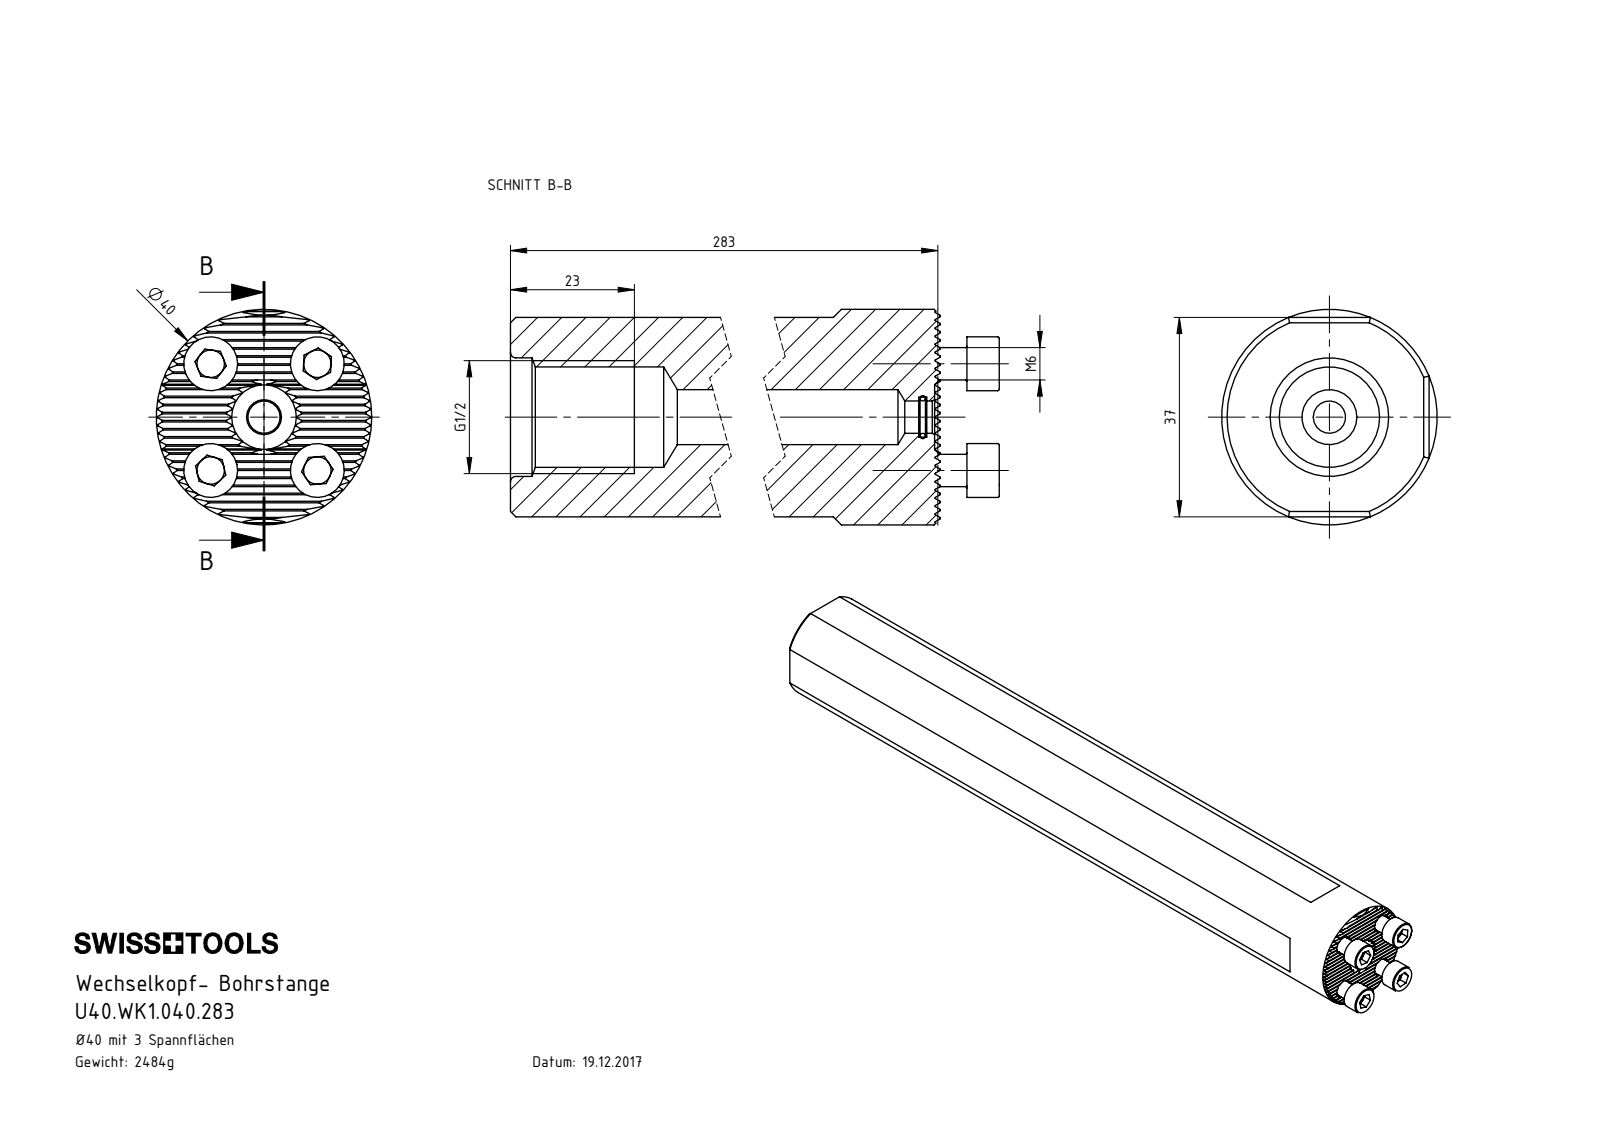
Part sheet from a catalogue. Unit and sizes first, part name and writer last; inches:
Units: inches
Overall size (bounding box): 11.591 × 1.575 × 1.575
Round holes (diameter × count): ⌀0.197 ×4, ⌀0.236 ×1, ⌀0.291 ×1, ⌀0.402 ×1, ⌀0.733 ×1, ⌀0.866 ×1
Round bosses / shafts (diameter × count): ⌀0.394 ×3, ⌀0.236 ×3, ⌀1.575 ×1
Partial cylindrical surfaces — rounded edges, fillets, slot ends (radius × count): R0.005 ×27
Main face-to-face distances: 1.457, 0.051, 0.102, 0.154, 0.205, 0.511, 0.358, 0.46, 0.307, 0.409
Hole centre spacings: 0.551, 0.78, 1.102
Volume: 19.26 in³ · Surface area: 79.07 in²
Bodies: 5 solids, 366 faces (218 planar, 86 cylindrical, 62 other)
Part name (STEP PRODUCT): U40-WK1.040.283_A; U40.WK1.040.283; DIN 3771 - 6x1; ISO 4762 - M6 x 16
STEP written by: SolidWorks 2017 (AUTOMOTIVE_DESIGN)
